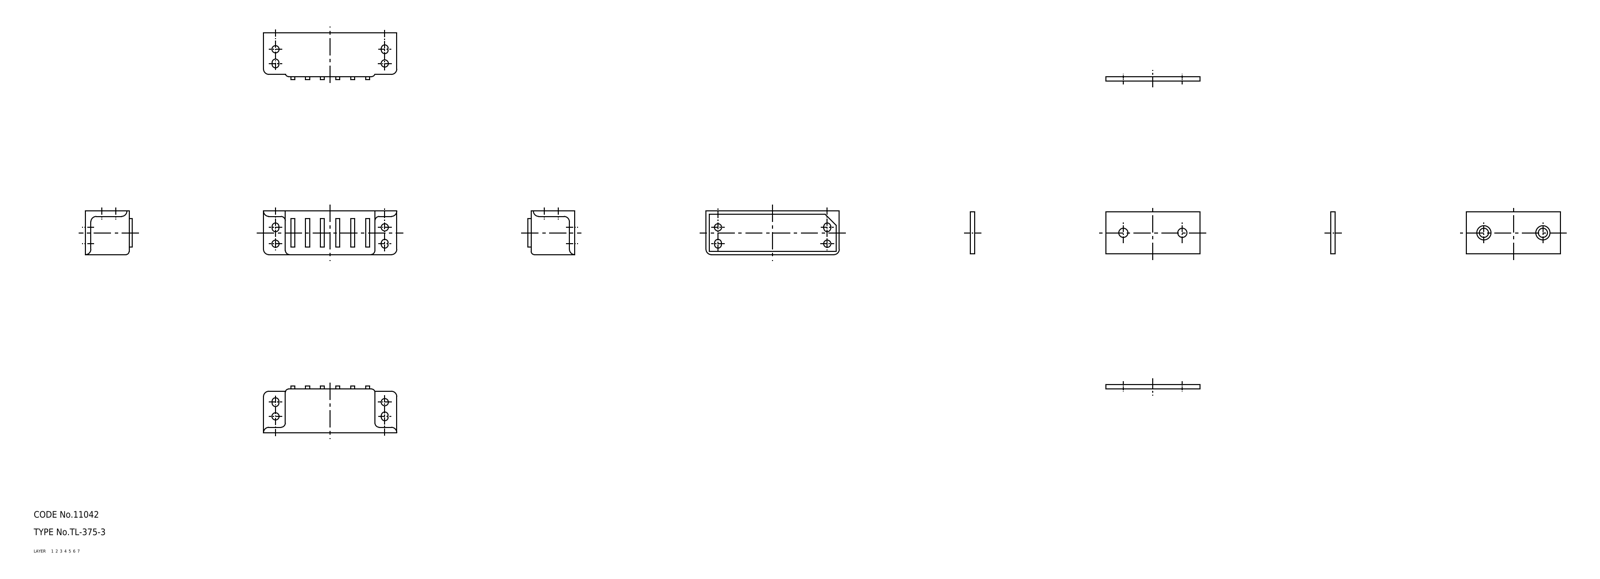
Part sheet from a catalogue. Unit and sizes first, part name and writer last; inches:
Units: inches
Overall size (bounding box): 2.402 × 1.85 × 0.787
Volume: 1.198 in³ · Surface area: 21.31 in²
Bodies: 8 solids, 165 faces (0 planar, 0 cylindrical, 165 other)
Part name (STEP PRODUCT): 67116095; 67116108; 67116121; 67116134 (+4 more)
STEP written by: CADfix (AUTOMOTIVE_DESIGN)
